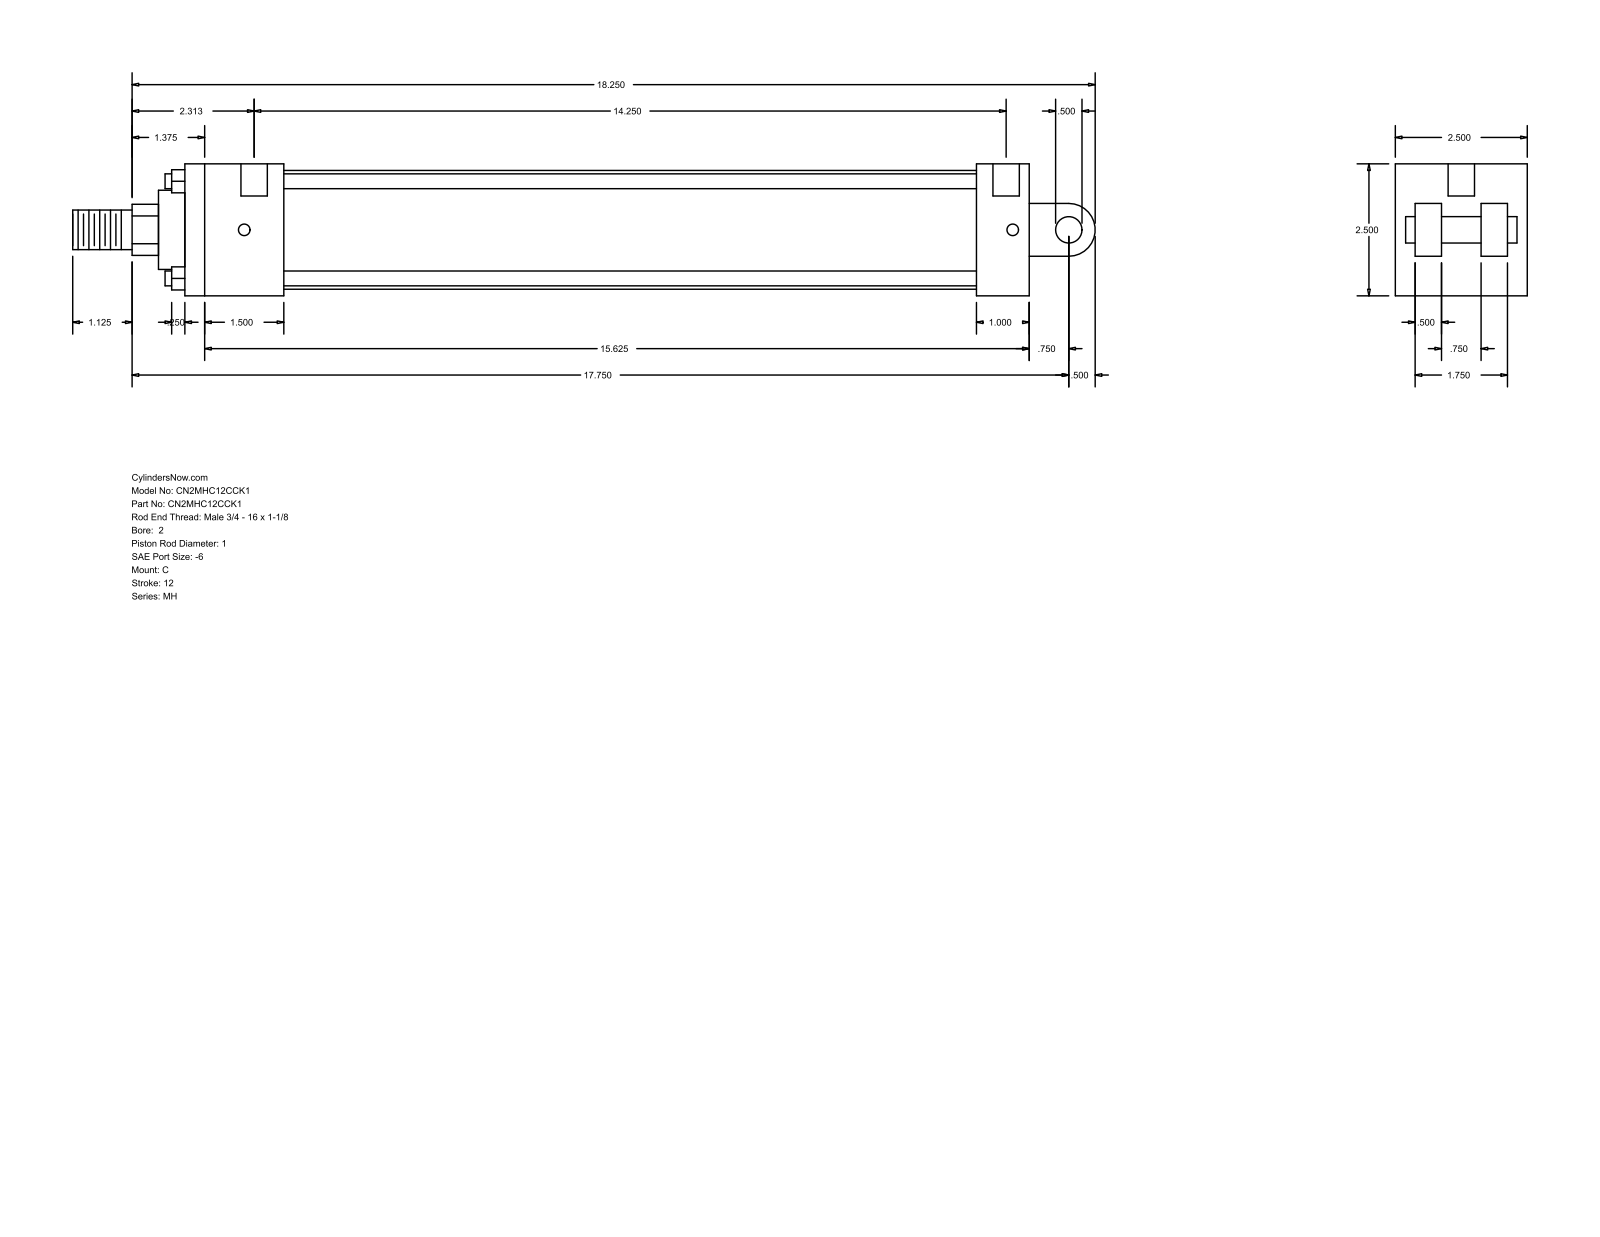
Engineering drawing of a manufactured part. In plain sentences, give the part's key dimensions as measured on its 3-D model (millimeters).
The part is named "MH_C__0200_1". Its 3-D file was written by "GSSL Pune (CONFIG_CONTROL_DESIGN)". It is 0 solids with 99 faces: 70 planar, 29 cylindrical and 0 other. Overall it measures 492.12 by 63.5 by 63.5 millimeters. Round holes: 4 of diameter 5.56, 2 of diameter 12.7. Round bosses or shafts: 4 of diameter 7.14, 1 of diameter 57.15, 1 of diameter 38.1, 1 of diameter 25.4, 1 of diameter 19.05, 1 of diameter 12.7. Partial cylindrical surfaces (rounded edges, fillets, slot ends): 1 of radius 12.29, 1 of radius 12.7. The main face-to-face distances are 63.5, 406.4, 12.7, 25.4, 47.63, 53.98, 9.52, 381, 333.37, 358.77. The hole center spacings are 369.88, 3.17, 4.76, 361.95, 365.12, 366.71.
